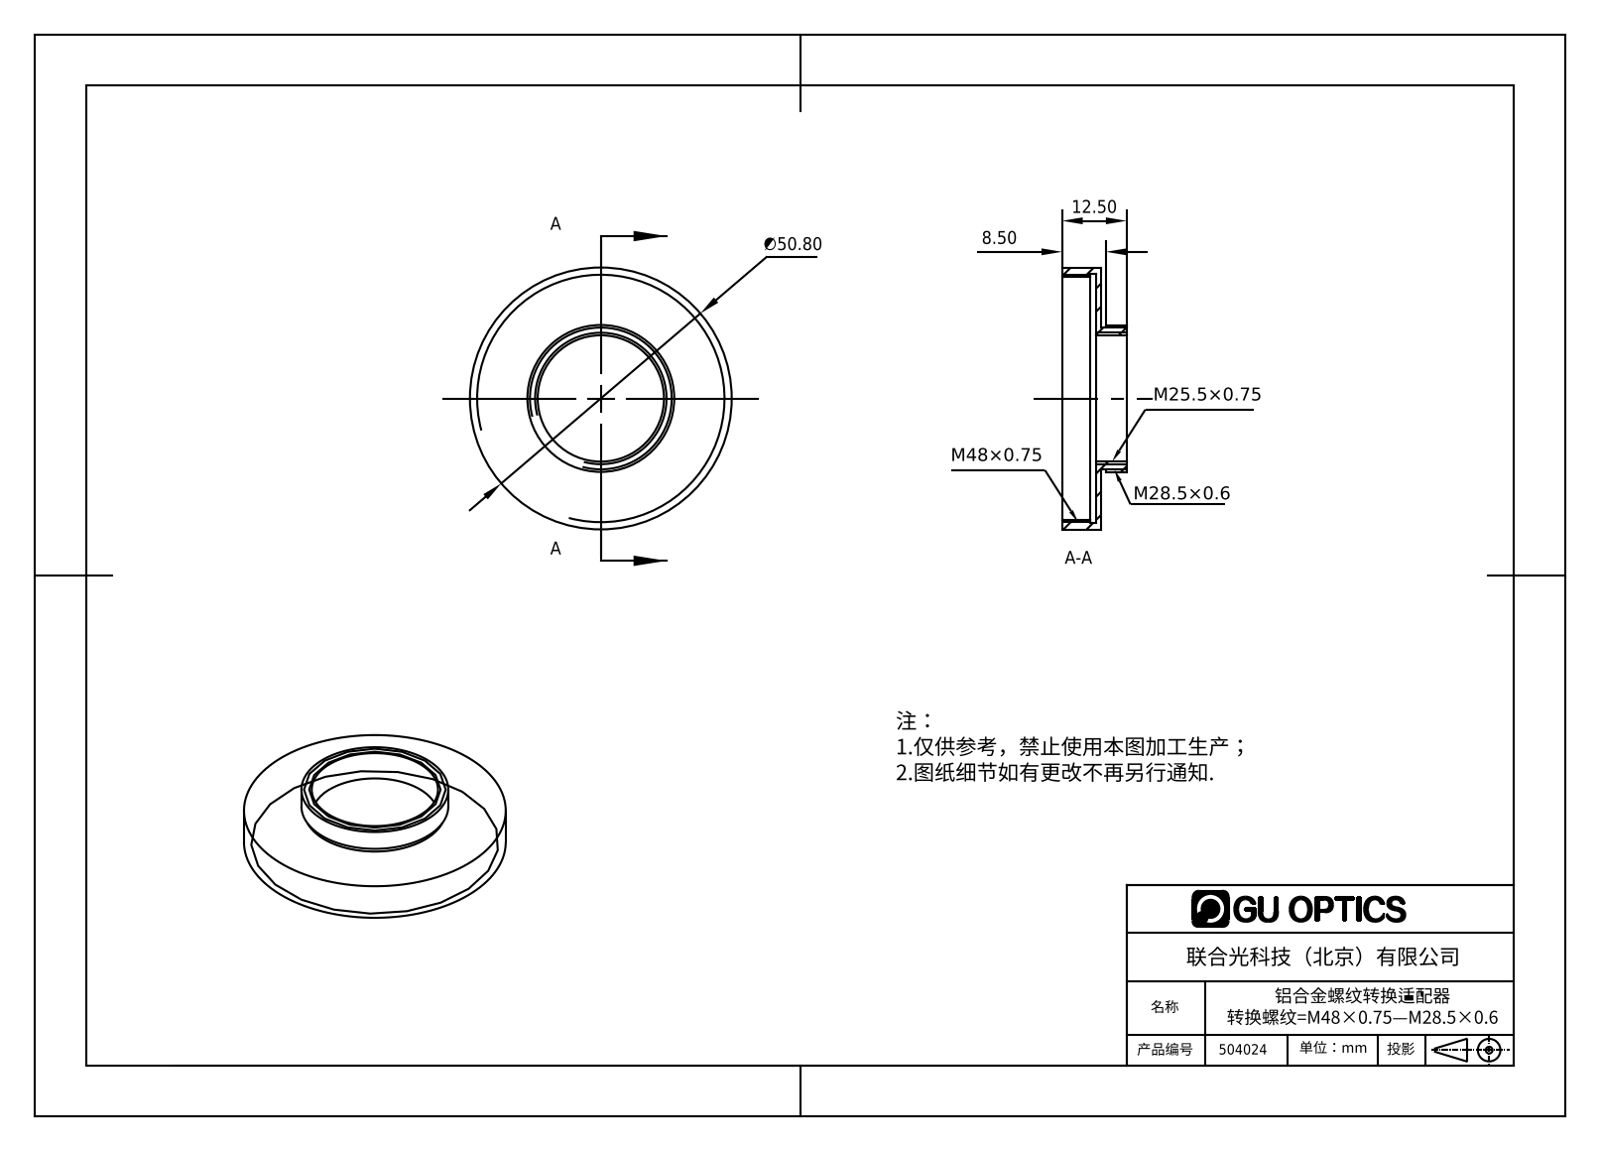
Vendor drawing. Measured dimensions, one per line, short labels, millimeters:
name: 504024
written by: SolidWorks 2016 (AUTOMOTIVE_DESIGN)
unit: mm
bodies: 1 solid, 18 faces (6 planar, 12 cylindrical, 0 other)
size: 50.8 × 50.8 × 12.5
volume: 4 151 mm³; area: 6 445 mm²
holes: 1× ⌀24.5, 1× ⌀47, 1× ⌀48.2
bosses: 1× ⌀50.8, 1× ⌀28.5, 1× ⌀27.5
face distances: 1, 6.5, 7.5, 12.5, 6, 5, 2, 5.5, 7, 8.5
